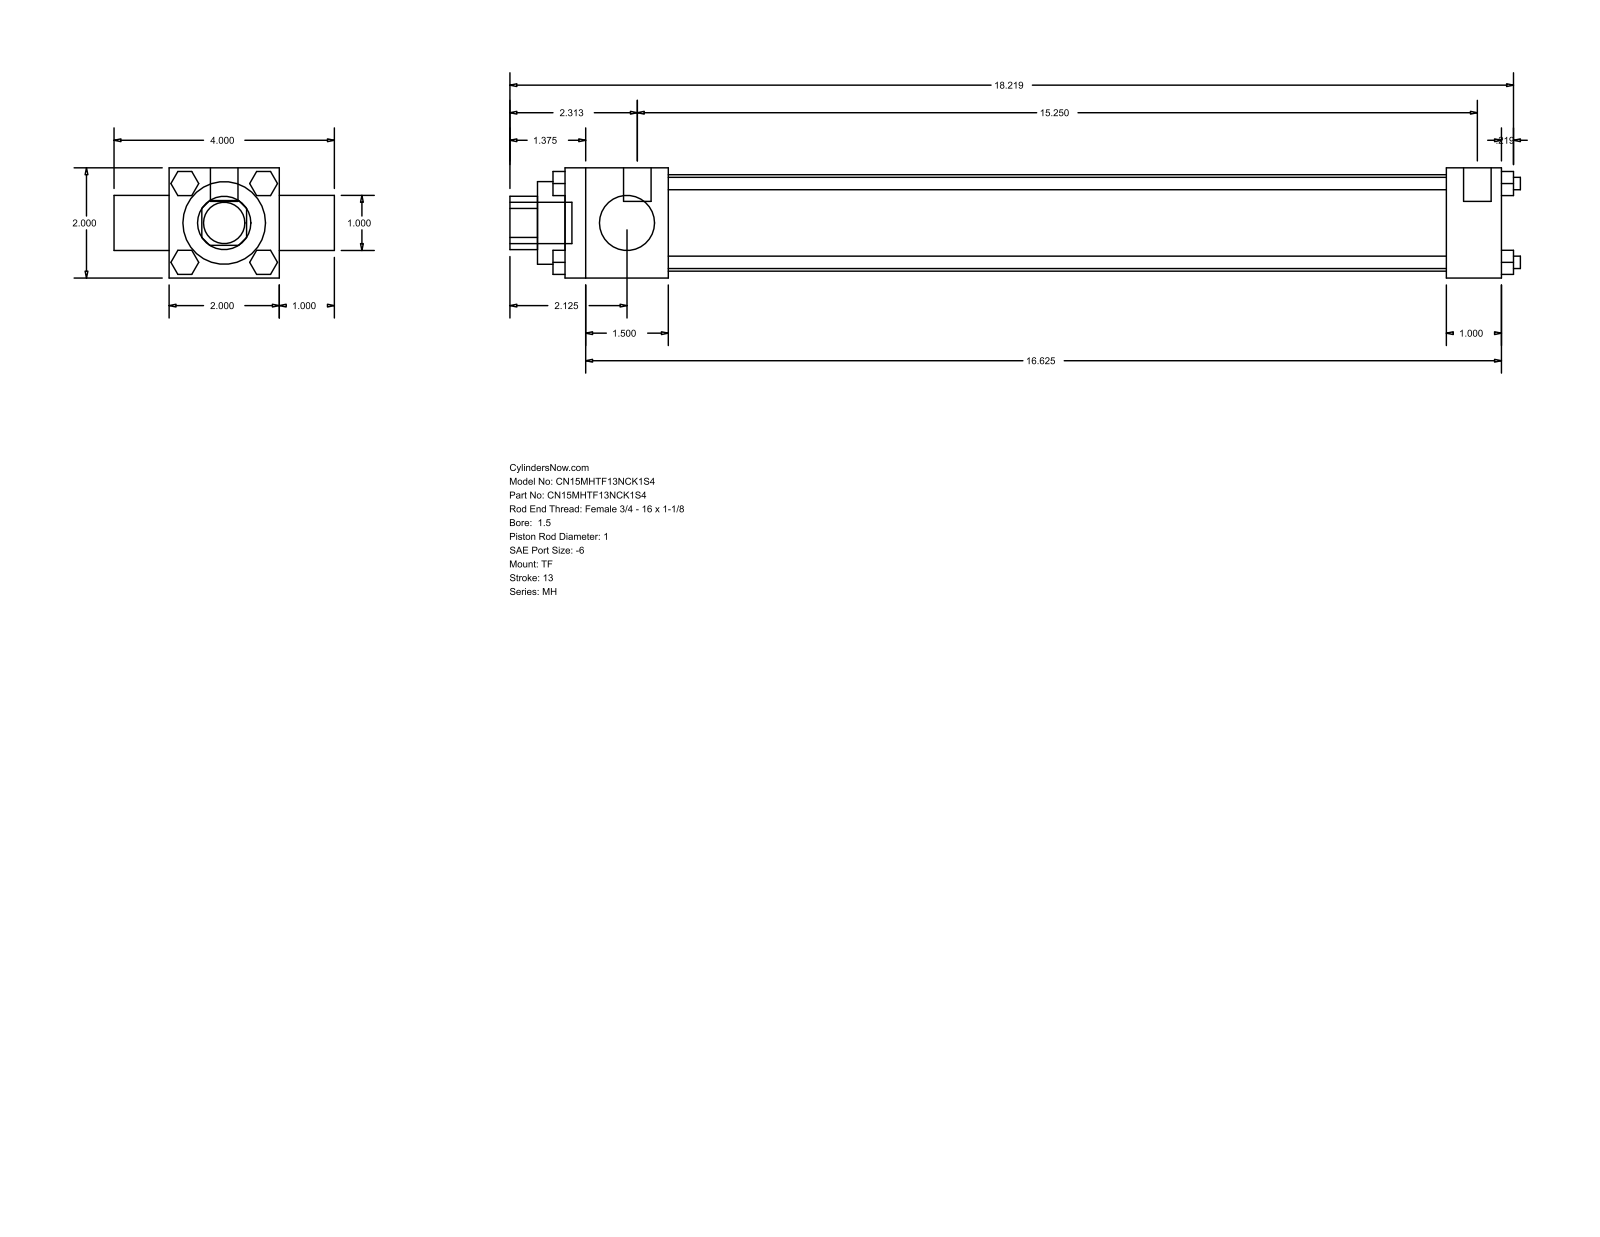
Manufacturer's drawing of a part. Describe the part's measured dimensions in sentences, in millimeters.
The part is named "MH_TF__0150_1". Its 3-D file was written by "GSSL Pune (CONFIG_CONTROL_DESIGN)". It is 0 solids with 120 faces: 92 planar, 28 cylindrical and 0 other. Overall it measures 465.93 by 101.6 by 50.8 millimeters. Round holes: 2 of diameter 25.4, 1 of diameter 38.1, 1 of diameter 44.45. Round bosses or shafts: 4 of diameter 5.71, 3 of diameter 5.56, 2 of diameter 12.7, 1 of diameter 19.05. Partial cylindrical surfaces (rounded edges, fillets, slot ends): 1 of radius 12.29. The main face-to-face distances are 50.8, 25.4, 431.8, 76.2, 47.63, 384.17, 406.4, 358.77, 437.36, 12.7.
